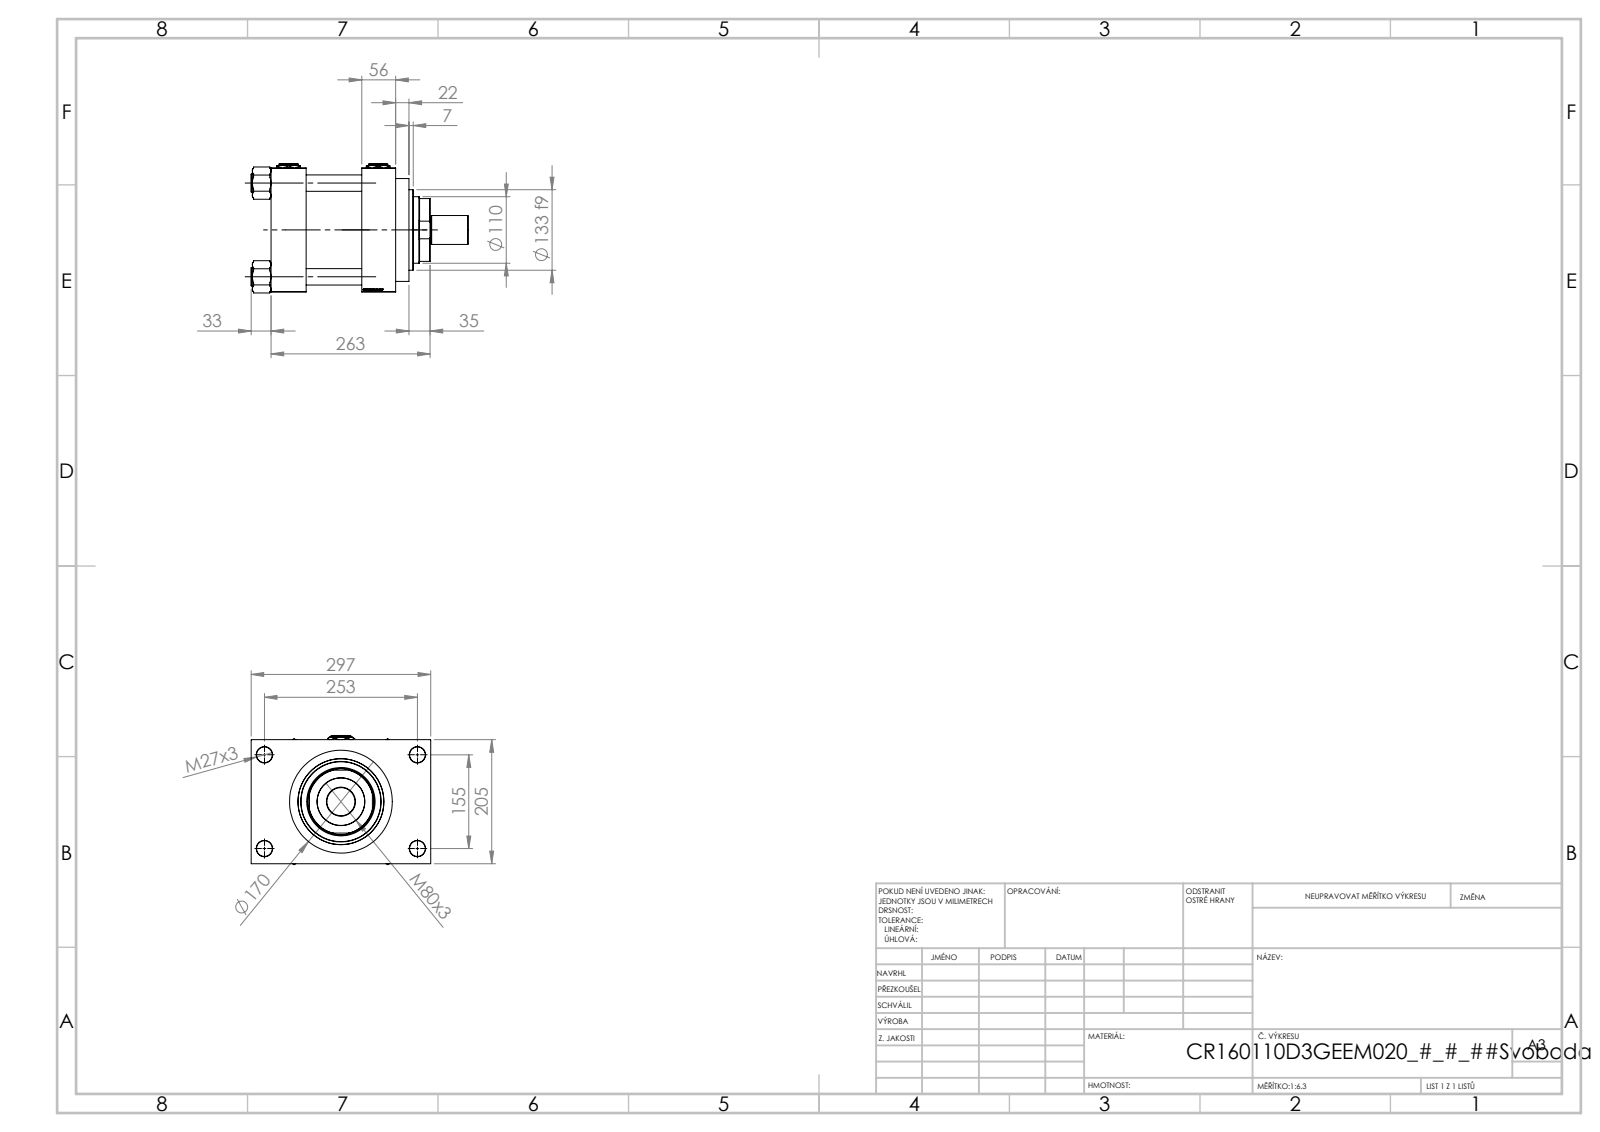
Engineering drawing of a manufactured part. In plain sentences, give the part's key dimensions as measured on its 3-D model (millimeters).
The part is named "V215CR_D_Body; V215CR_D_TYCINKA; NUT_M5_D; V215CR_VCP_D (+3 more)". Its 3-D file was written by "SolidWorks 2019 (CONFIG_CONTROL_DESIGN)". It is 14 solids with 1267 faces: 597 planar, 104 cylindrical and 566 other. Overall it measures 359 by 297 by 213.57 millimeters. Its volume is 8 248 000 cubic millimeters and its surface area 799 388 square millimeters. Round holes: 4 of diameter 26, 4 of diameter 27, 2 of diameter 7, 2 of diameter 33.24, 2 of diameter 45, 1 of diameter 78.5, 1 of diameter 110, 1 of diameter 113, 1 of diameter 120, 1 of diameter 142, 1 of diameter 160. Round bosses or shafts: 4 of diameter 30, 1 of diameter 170, 1 of diameter 166, 1 of diameter 133, 1 of diameter 48, 1 of diameter 46. Partial cylindrical surfaces (rounded edges, fillets, slot ends): 1 of radius 54. The main face-to-face distances are 58, 150, 92, 205, 148, 56, 206, 46, 251, 72. The hole center spacings are 49.05, 109.53, 148.35, 154.9, 162.53, 203.95, 256.13, 155.
